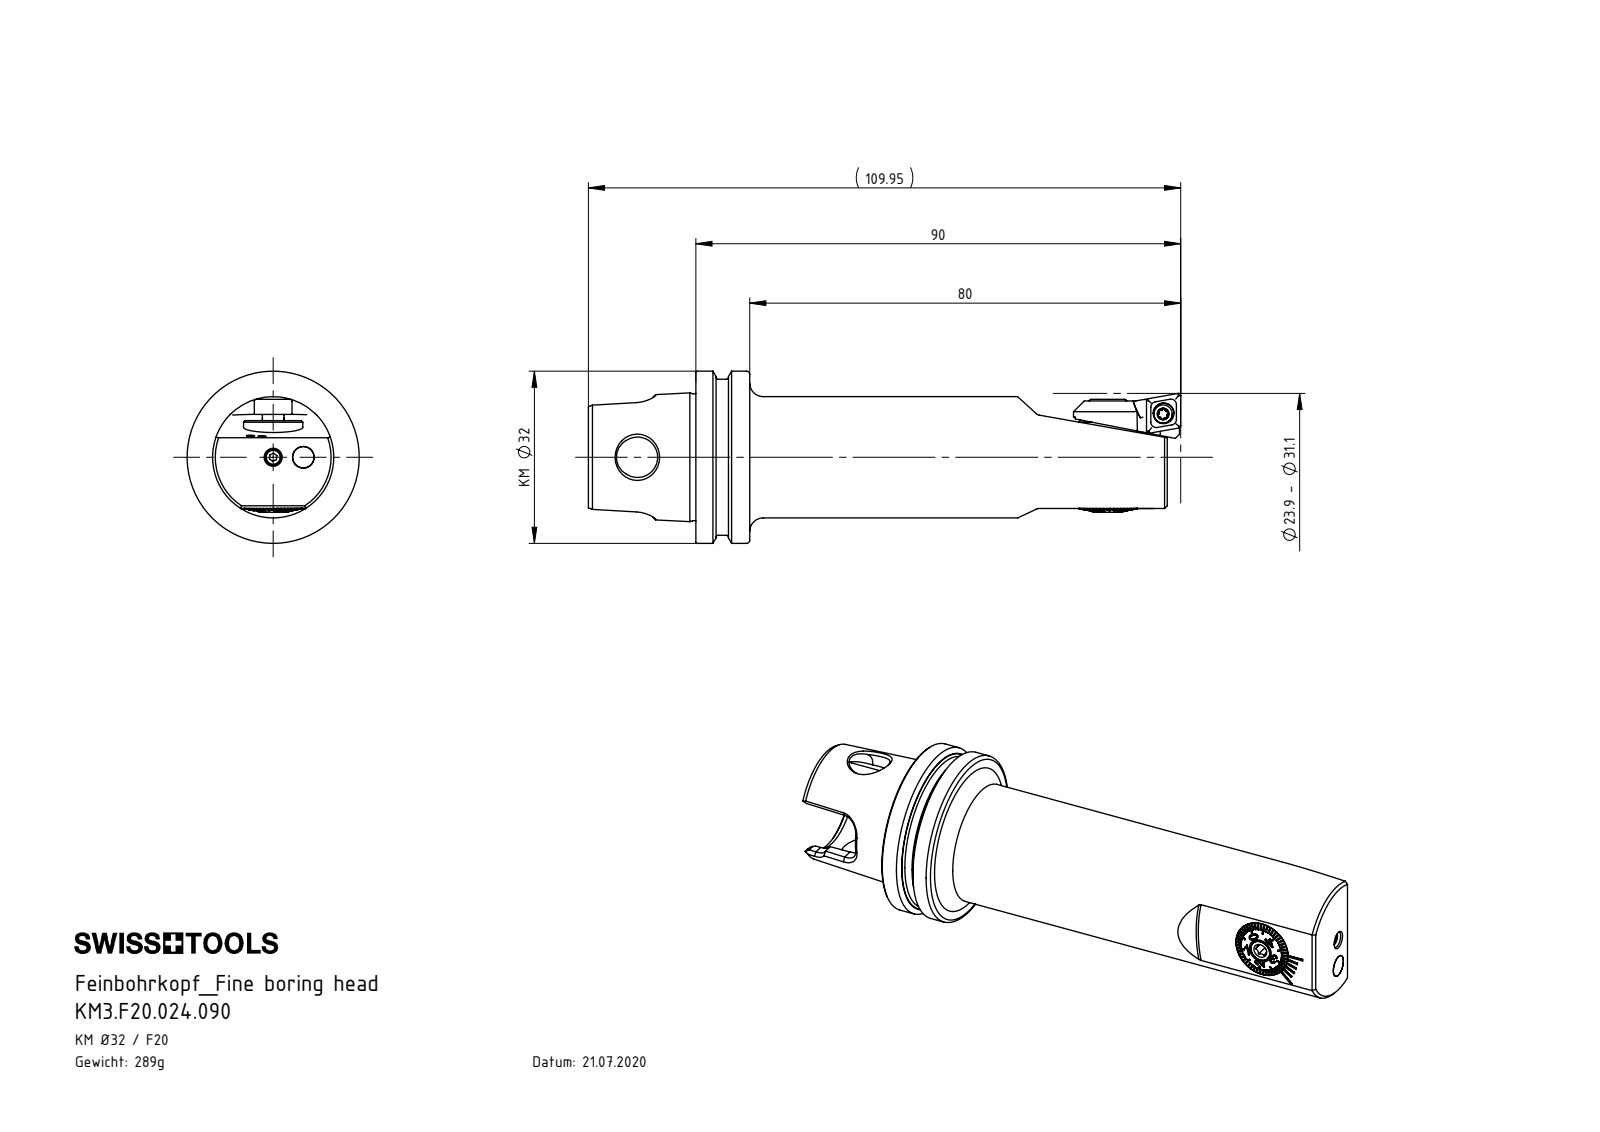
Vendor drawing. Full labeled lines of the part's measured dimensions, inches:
Part name (STEP PRODUCT): F20-BG2.011.004_A; F20-BG2.008.009_A; ISO 4762 - M1.4 x 6; KM3.F20.AA4.090 (+8 more)
STEP written by: SolidWorks 2017 (AUTOMOTIVE_DESIGN)
Units: inches
Bodies: 13 solids, 564 faces (303 planar, 69 cylindrical, 192 other)
Overall size (bounding box): 4.23 × 1.258 × 1.258
Volume: 2.258 in³ · Surface area: 22.94 in²
Round holes (diameter × count): ⌀0.083 ×4, ⌀0.059 ×2, ⌀0.118 ×2, ⌀0.13 ×2, ⌀0.043 ×1, ⌀0.075 ×1, ⌀0.157 ×1, ⌀0.165 ×1, ⌀0.177 ×1, ⌀0.213 ×1, ⌀0.236 ×1, ⌀0.244 ×1
Round bosses / shafts (diameter × count): ⌀0.157 ×2, ⌀0.156 ×2, ⌀1.258 ×1, ⌀1.14 ×1, ⌀0.886 ×1, ⌀0.433 ×1, ⌀0.432 ×1, ⌀0.427 ×1
Partial cylindrical surfaces — rounded edges, fillets, slot ends (radius × count): R0.118 ×3, R0.012 ×2, R0.049 ×2, R0.079 ×2, R0.139 ×2, R0.148 ×1
Main face-to-face distances: 3.445, 0.394, 3.051, 0.02, 0.374, 3.425, 0.146, 0.079, 0.098, 0.059
Hole centre spacings: 0.212, 0.22, 0.343
